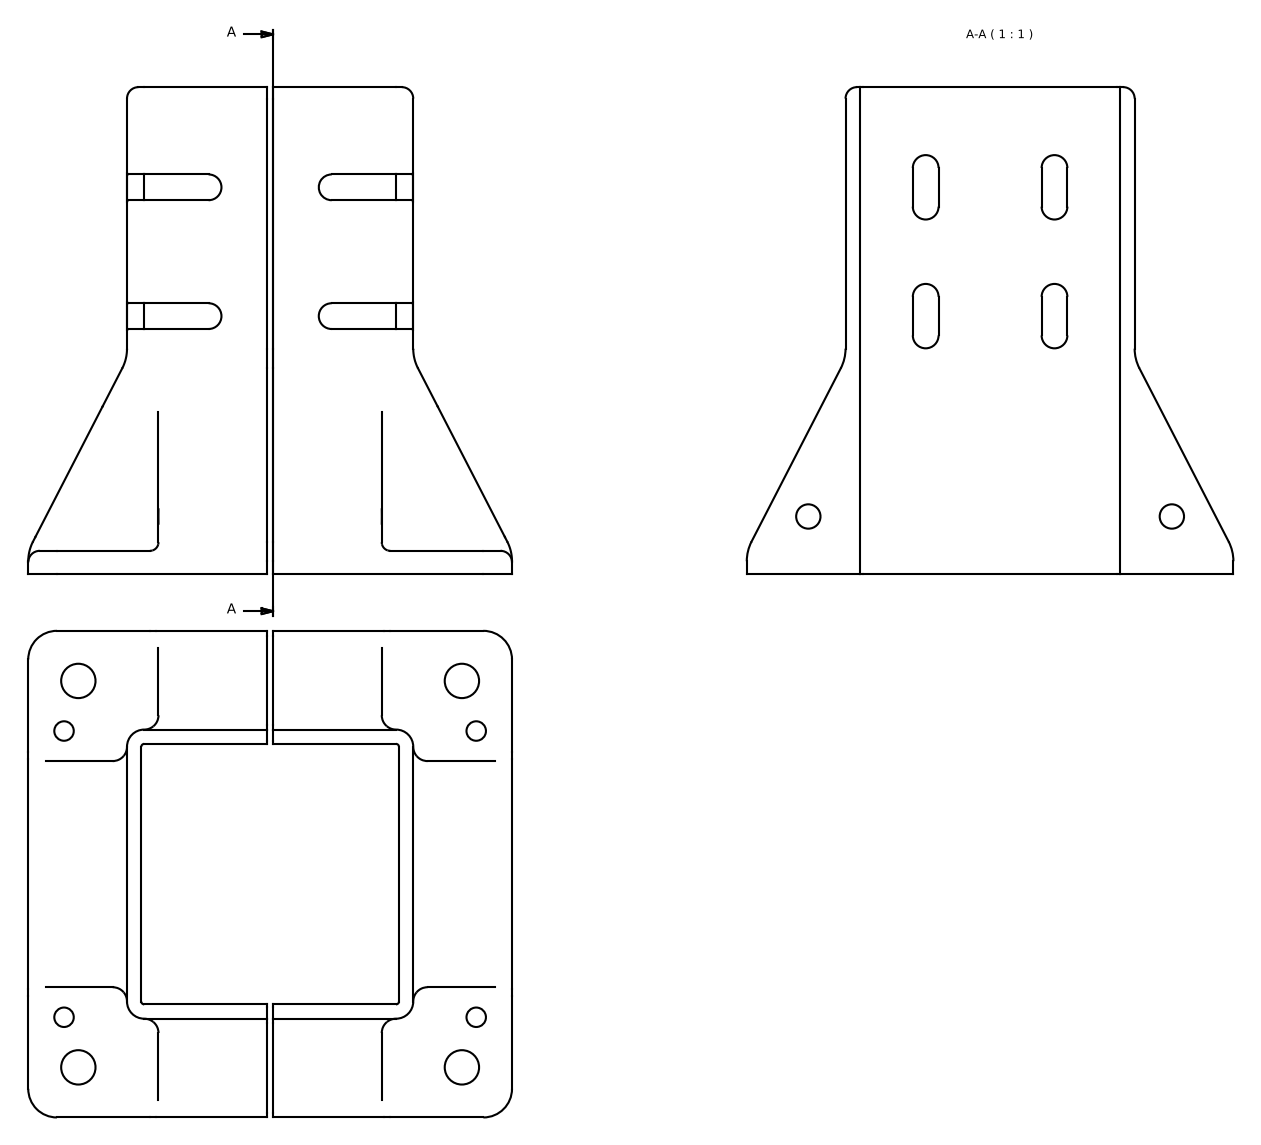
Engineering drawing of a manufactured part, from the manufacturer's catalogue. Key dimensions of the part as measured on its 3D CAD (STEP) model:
Part name (STEP PRODUCT): CPDFS0000007
STEP written by: Autodesk Inventor 2019 (AUTOMOTIVE_DESIGN)
Units: millimetres
Bodies: 2 solids, 424 faces (114 planar, 178 cylindrical, 132 other)
Overall size (bounding box): 170 × 170 × 169
Volume: 534 900 mm³ · Surface area: 208 442 mm²
Round holes (diameter × count): ⌀6.8 ×4, ⌀12 ×4, ⌀8.5 ×2, ⌀17 ×2
Partial cylindrical surfaces — rounded edges, fillets, slot ends (radius × count): R2 ×40, R0.5 ×16, R4 ×16, R4.5 ×12, R5 ×8, R15 ×8, R1 ×4, R3 ×4
Main face-to-face distances: 5, 95, 96, 90, 91, 44, 51, 100, 101, 11
Hole centre spacings: 18.2, 117.61, 140.1, 182.01, 100, 134, 135, 144
